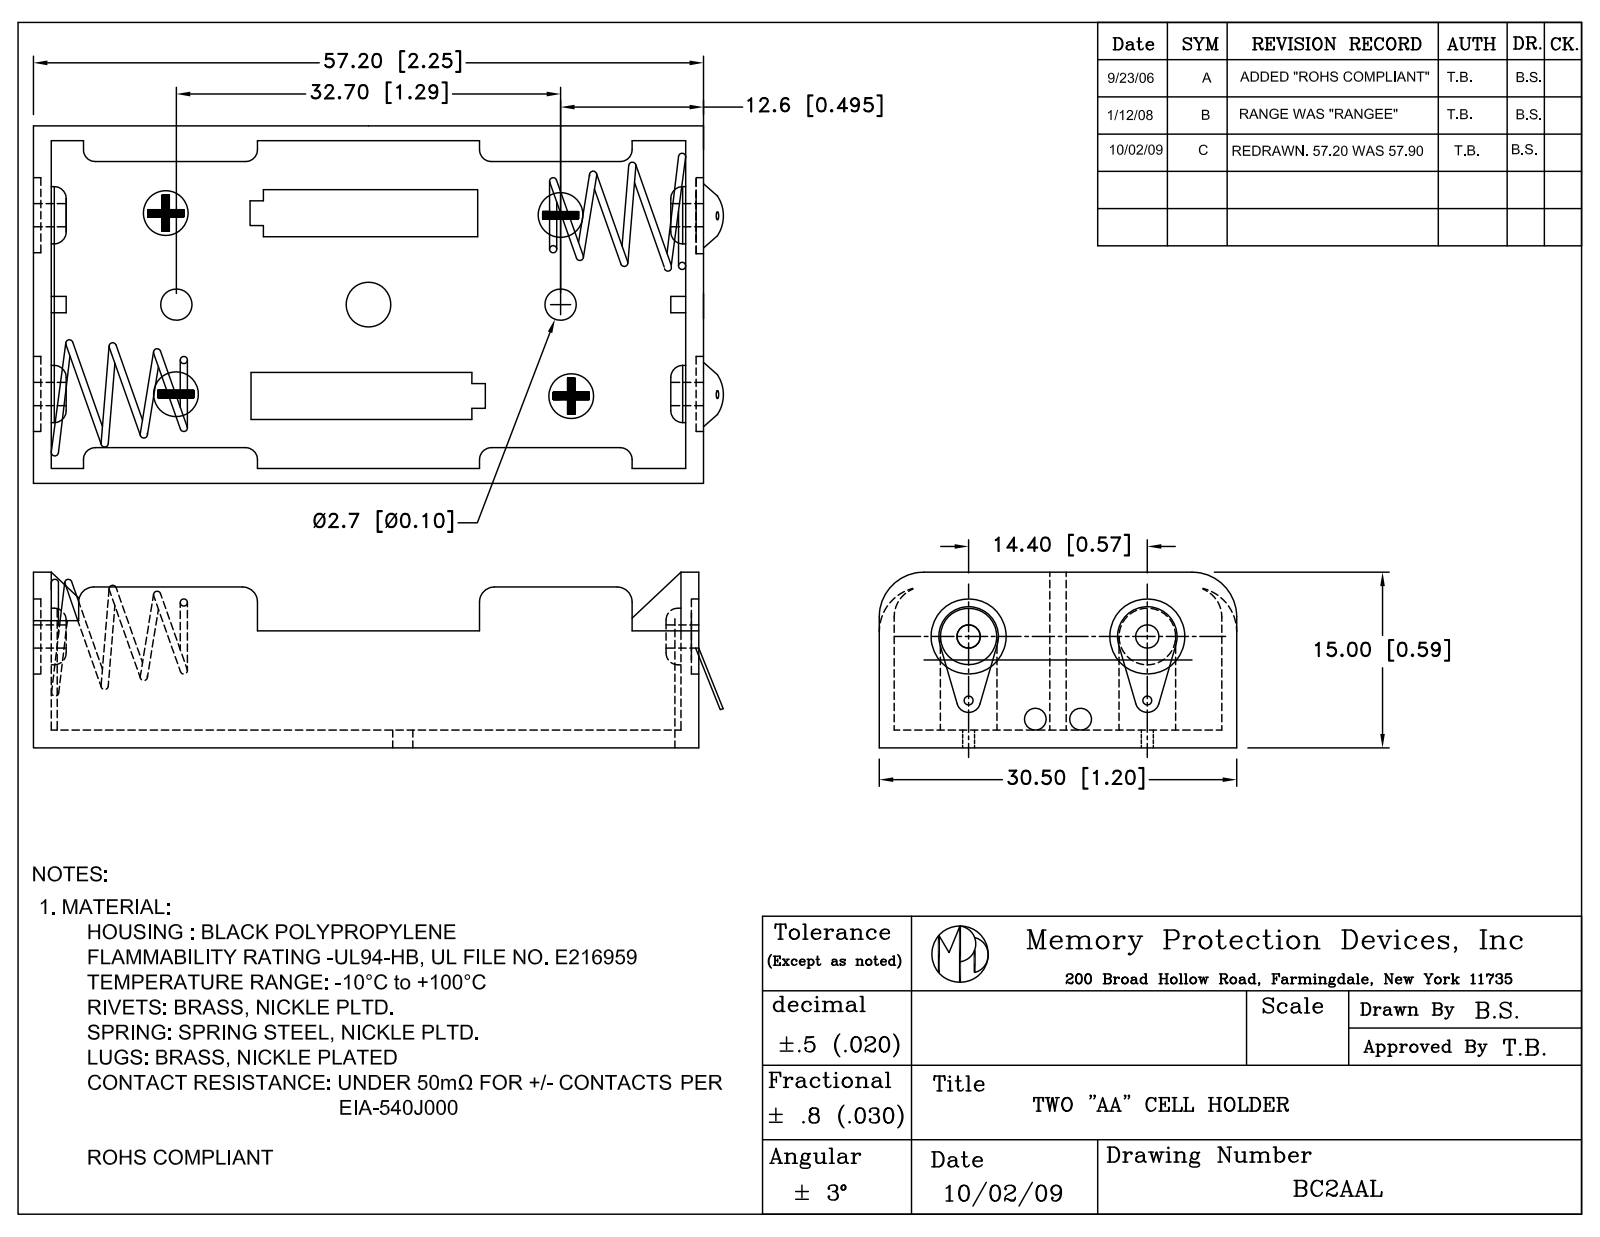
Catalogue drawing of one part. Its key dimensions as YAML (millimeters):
part_name: "BC2AAL"
step_written_by: "SolidWorks 2021 (AUTOMOTIVE_DESIGN)"
units: millimeters
bodies: {solids: 6, faces: 354, planar: 166, cylindrical: 132, other: 56}
overall_size: [60.73, 30.5, 15]
volume: 4510
surface_area: 8538
round_holes:
  - {diameter: 3.7, count: 4}
  - {diameter: 1.92, count: 3}
  - {diameter: 0.8, count: 2}
  - {diameter: 1.4, count: 2}
  - {diameter: 2, count: 2}
  - {diameter: 2.3, count: 2}
  - {diameter: 2.7, count: 2}
  - {diameter: 3, count: 2}
  - {diameter: 7.6, count: 2}
  - {diameter: 3.65, count: 1}
round_bosses_or_shafts:
  - {diameter: 4.7, count: 4}
  - {diameter: 6.2, count: 2}
  - {diameter: 3.5, count: 2}
  - {diameter: 0.6, count: 2}
  - {diameter: 0.7, count: 1}
partial_cylinders:
  - {radius: 2.5, count: 8}
  - {radius: 1.4, count: 2}
  - {radius: 2.85, count: 2}
  - {radius: 3, count: 2}
  - {radius: 3.15, count: 2}
  - {radius: 4, count: 2}
  - {radius: 9, count: 1}
  - {radius: 9.31, count: 1}
face_to_face_distances: [1.1, 1.55, 29.4, 56.9, 55.8, 28.3, 30.5, 58, 0.31, 57.69]
hole_center_spacings: [20.47, 7.86, 10.06, 15.25, 36.21, 38, 40.95, 3.1]
